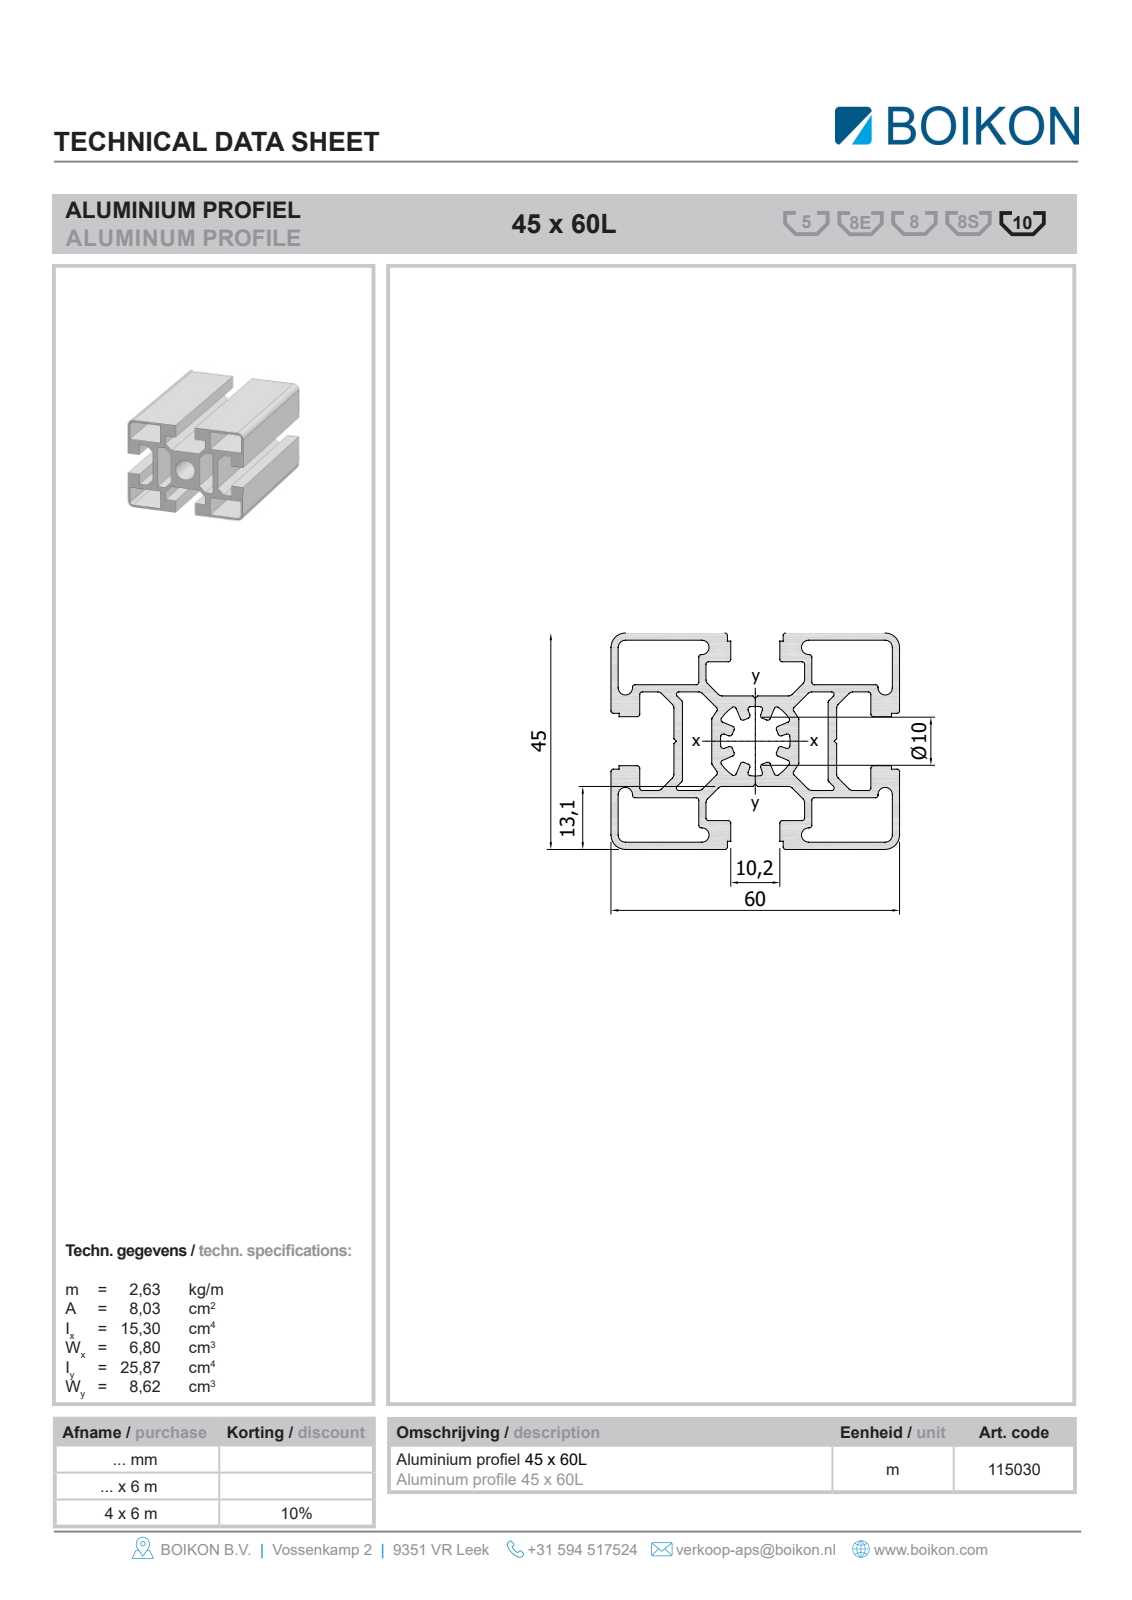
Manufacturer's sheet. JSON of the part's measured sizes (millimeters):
{"part_name": "Root; 11503045x60LBOIKON0", "step_written_by": "HiCAD 2013 1802.4 Build 509 (AUTOMOTIVE_DESIGN)", "units": "millimeters", "bodies": {"solids": 1, "faces": 83, "planar": 74, "cylindrical": 9, "other": 0}, "overall_size": [1000, 60, 45], "volume_mm3": 979226, "surface_area_mm2": 711457, "round_holes": [[10, 1]], "partial_cylinders_radius": [[1.5, 4], [3, 4]], "face_to_face_distances": [1, 7.1, 43, 10, 35, 44, 9, 34, 21.7, 13.1]}
